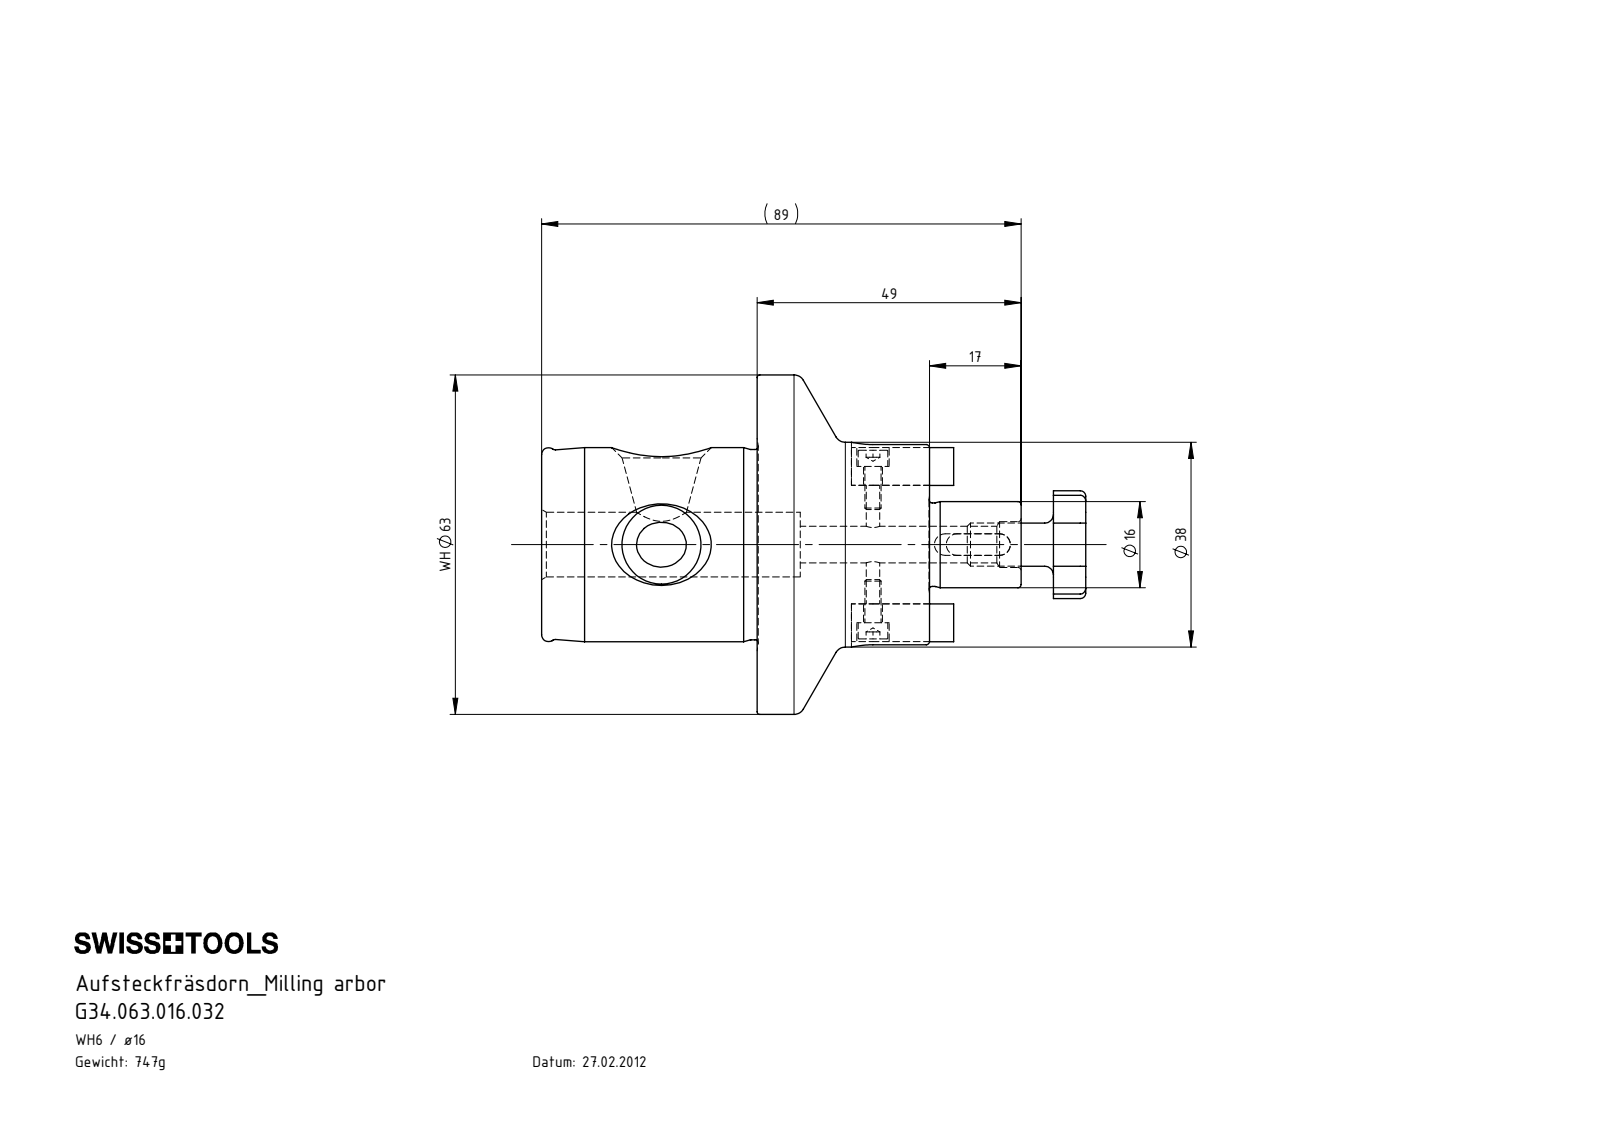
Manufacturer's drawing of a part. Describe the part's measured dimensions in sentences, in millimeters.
The part is named "ISO 4762 - M3 x 8; D16-ER3.001.014_A; WH6.D16.001.032; D16-ER2.002.008_A (+2 more)". Its 3-D file was written by "SolidWorks 2022 (AUTOMOTIVE_DESIGN)". It is 7 solids with 210 faces: 71 planar, 60 cylindrical and 79 other. Overall it measures 101 by 63 by 63 millimeters. Its volume is 95 098 cubic millimeters and its surface area 22 227 square millimeters. Round holes: 1 of diameter 2.5, 1 of diameter 3.5, 1 of diameter 6, 1 of diameter 6.8, 1 of diameter 8.5, 1 of diameter 12. Round bosses or shafts: 1 of diameter 63, 1 of diameter 38, 1 of diameter 36, 1 of diameter 35.3, 1 of diameter 16, 1 of diameter 15.5, 1 of diameter 8, 1 of diameter 5.5. Partial cylindrical surfaces (rounded edges, fillets, slot ends): 7 of radius 2, 1 of radius 4, 1 of radius 10. The main face-to-face distances are 40, 32, 72, 8, 29, 22, 7, 6, 101, 61.
